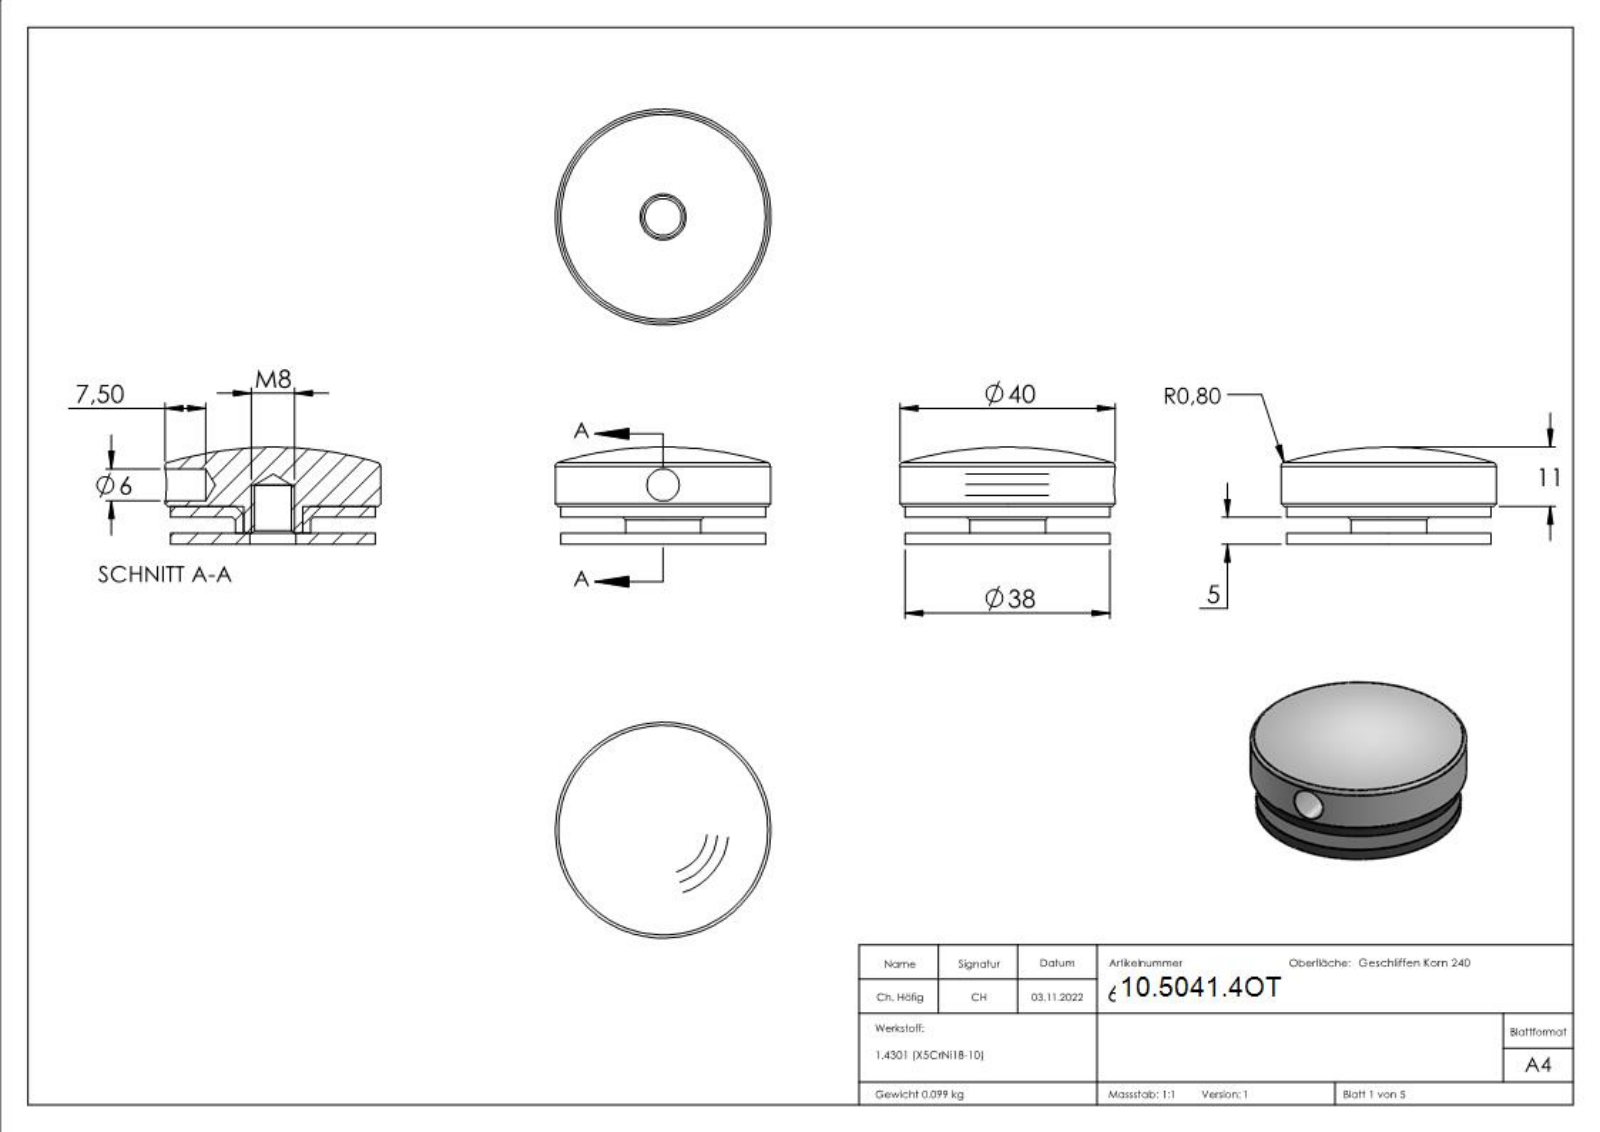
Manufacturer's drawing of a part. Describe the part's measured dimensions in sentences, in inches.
The part is named "60230-240-OT Teil1_60230-240-OT Teil1; 60230-240-OT; 60230-240-OT Teil2_60230-240-OT Teil2; 60230-240-OT Teil3_60230-240-OT Teil3". Its 3-D file was written by "SolidWorks 2018 (CONFIG_CONTROL_DESIGN)". It is 3 solids with 273 faces: 137 planar, 9 cylindrical and 127 other. Overall it measures 1.575 by 1.575 by 0.709 inches. Its volume is 0.988 cubic inches and its surface area 13.98 square inches. Round holes: 1 of diameter 0.236, 1 of diameter 0.268, 1 of diameter 0.335, 1 of diameter 0.433. Round bosses or shafts: 1 of diameter 1.575, 1 of diameter 1.496, 1 of diameter 0.551. The main face-to-face distances are 0.197, 0.079, 0.276, 0.118, 0.28, 0.201, 0.083, 0.07, 0.033, 0.017.
